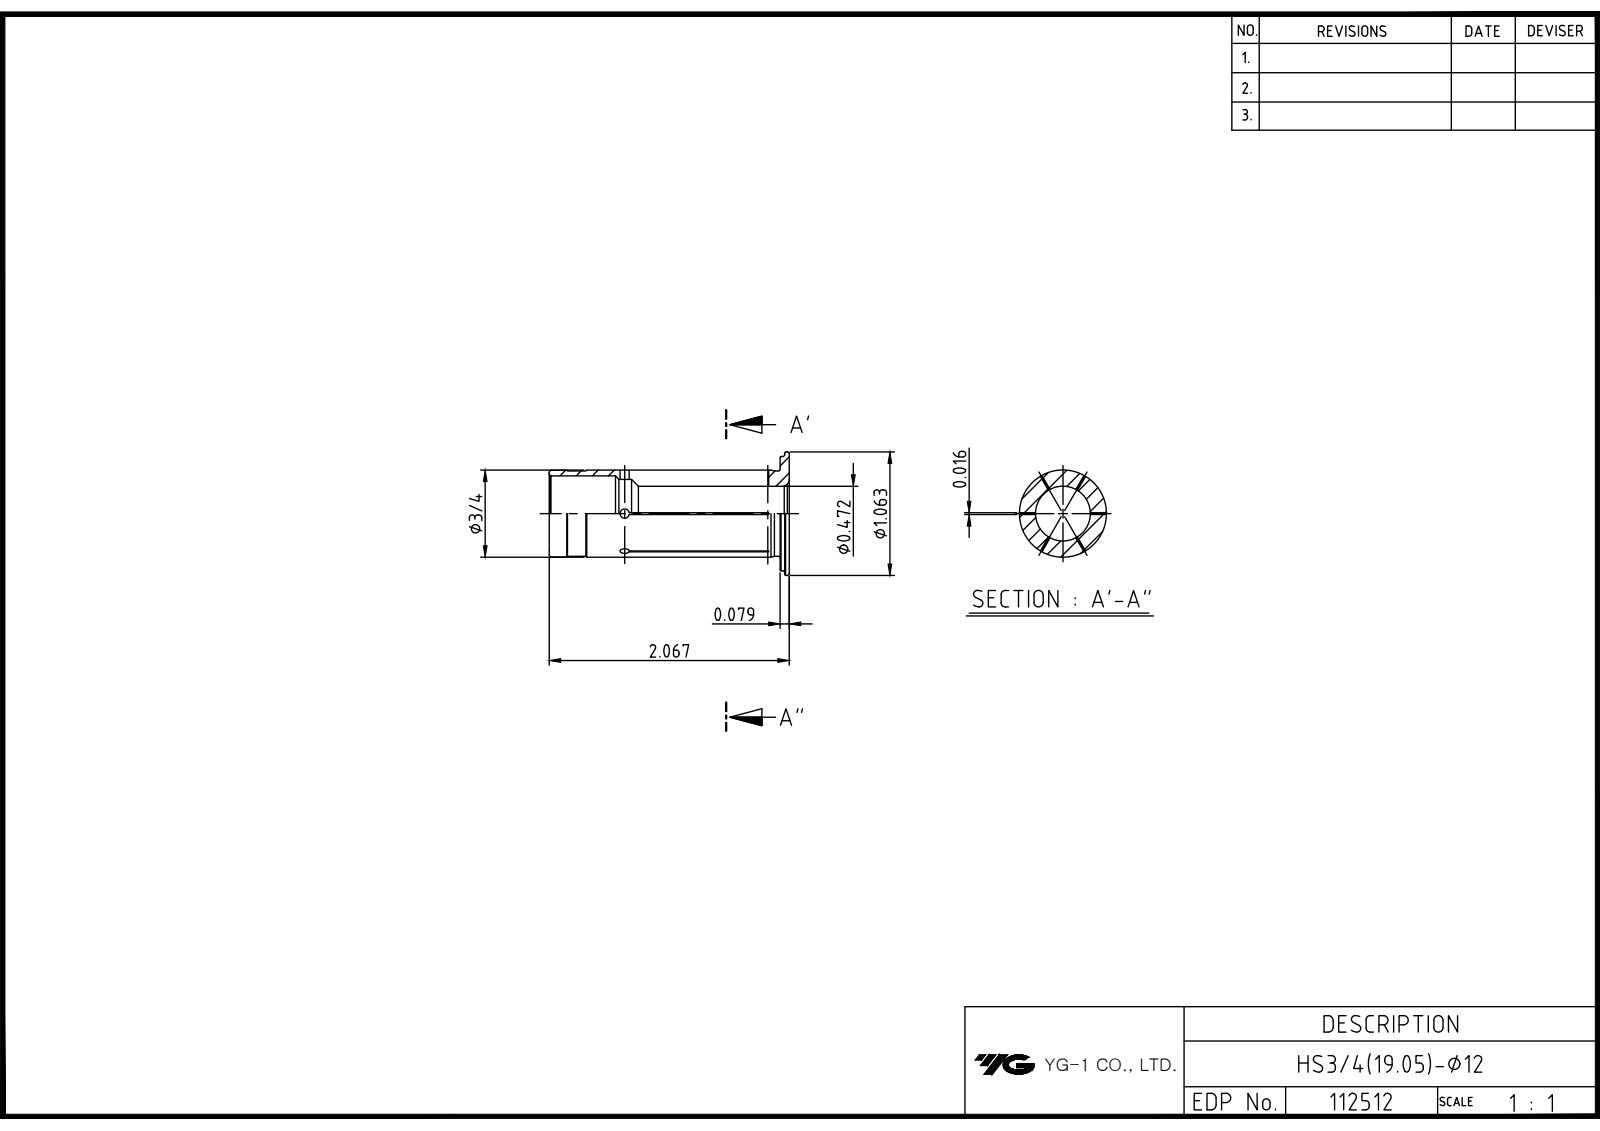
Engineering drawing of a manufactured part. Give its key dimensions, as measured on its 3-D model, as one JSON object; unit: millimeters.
{"part_name": "LO-HS19.05-12", "step_written_by": "Autodesk Inventor 2022 (AUTOMOTIVE_DESIGN)", "units": "millimeters", "bodies": {"solids": 1, "faces": 12, "planar": 4, "cylindrical": 6, "other": 2}, "overall_size": [52.5, 27, 27], "volume_mm3": 7777, "surface_area_mm2": 6272, "round_holes": [[12, 1], [15, 1], [16.5, 1]], "round_bosses_or_shafts": [[27, 1], [25, 1], [19.05, 1]], "face_to_face_distances": [2, 1, 50.5, 51.5, 52.5]}
